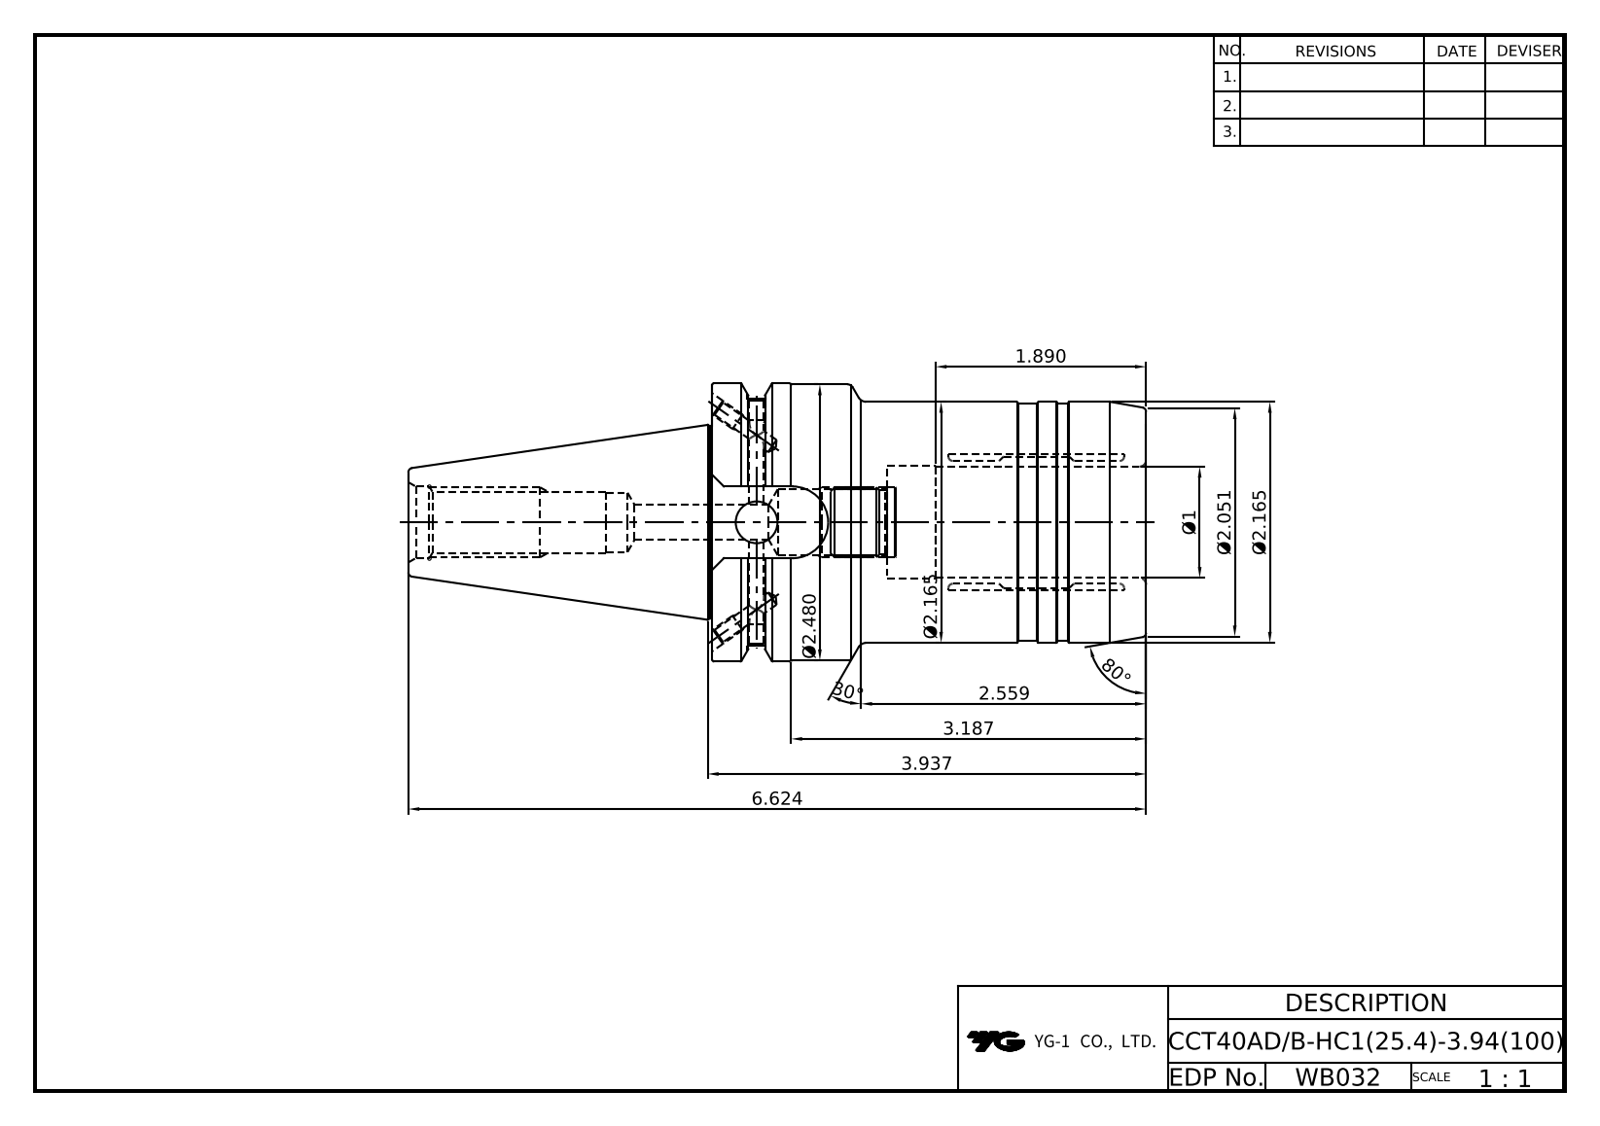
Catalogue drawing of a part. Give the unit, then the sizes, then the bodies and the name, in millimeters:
Units: millimetres
Overall size (bounding box): 168.25 × 63.5 × 63
Round holes (diameter × count): ⌀8 ×1, ⌀9.53 ×1, ⌀13.5 ×1, ⌀14 ×1, ⌀15.1 ×1, ⌀15.88 ×1, ⌀16 ×1, ⌀16.3 ×1, ⌀25.4 ×1, ⌀25.8 ×1
Round bosses / shafts (diameter × count): ⌀63.5 ×1, ⌀63 ×1, ⌀56.3 ×1, ⌀55 ×1, ⌀54 ×1, ⌀43.8 ×1
Partial cylindrical surfaces — rounded edges, fillets, slot ends (radius × count): R7.69 ×1
Main face-to-face distances: 99, 40, 59, 47.6, 69.25, 109.25, 168.25, 16.38, 4.8, 64.45
Volume: 272 472 mm³ · Surface area: 42 253 mm²
Bodies: 1 solid, 137 faces (37 planar, 42 cylindrical, 58 other)
Part name (STEP PRODUCT): CCT40ADB-SHANK
STEP written by: CREO PARAMETRIC BY PTC INC, 2018500 (CONFIG_CONTROL_DESIGN)
